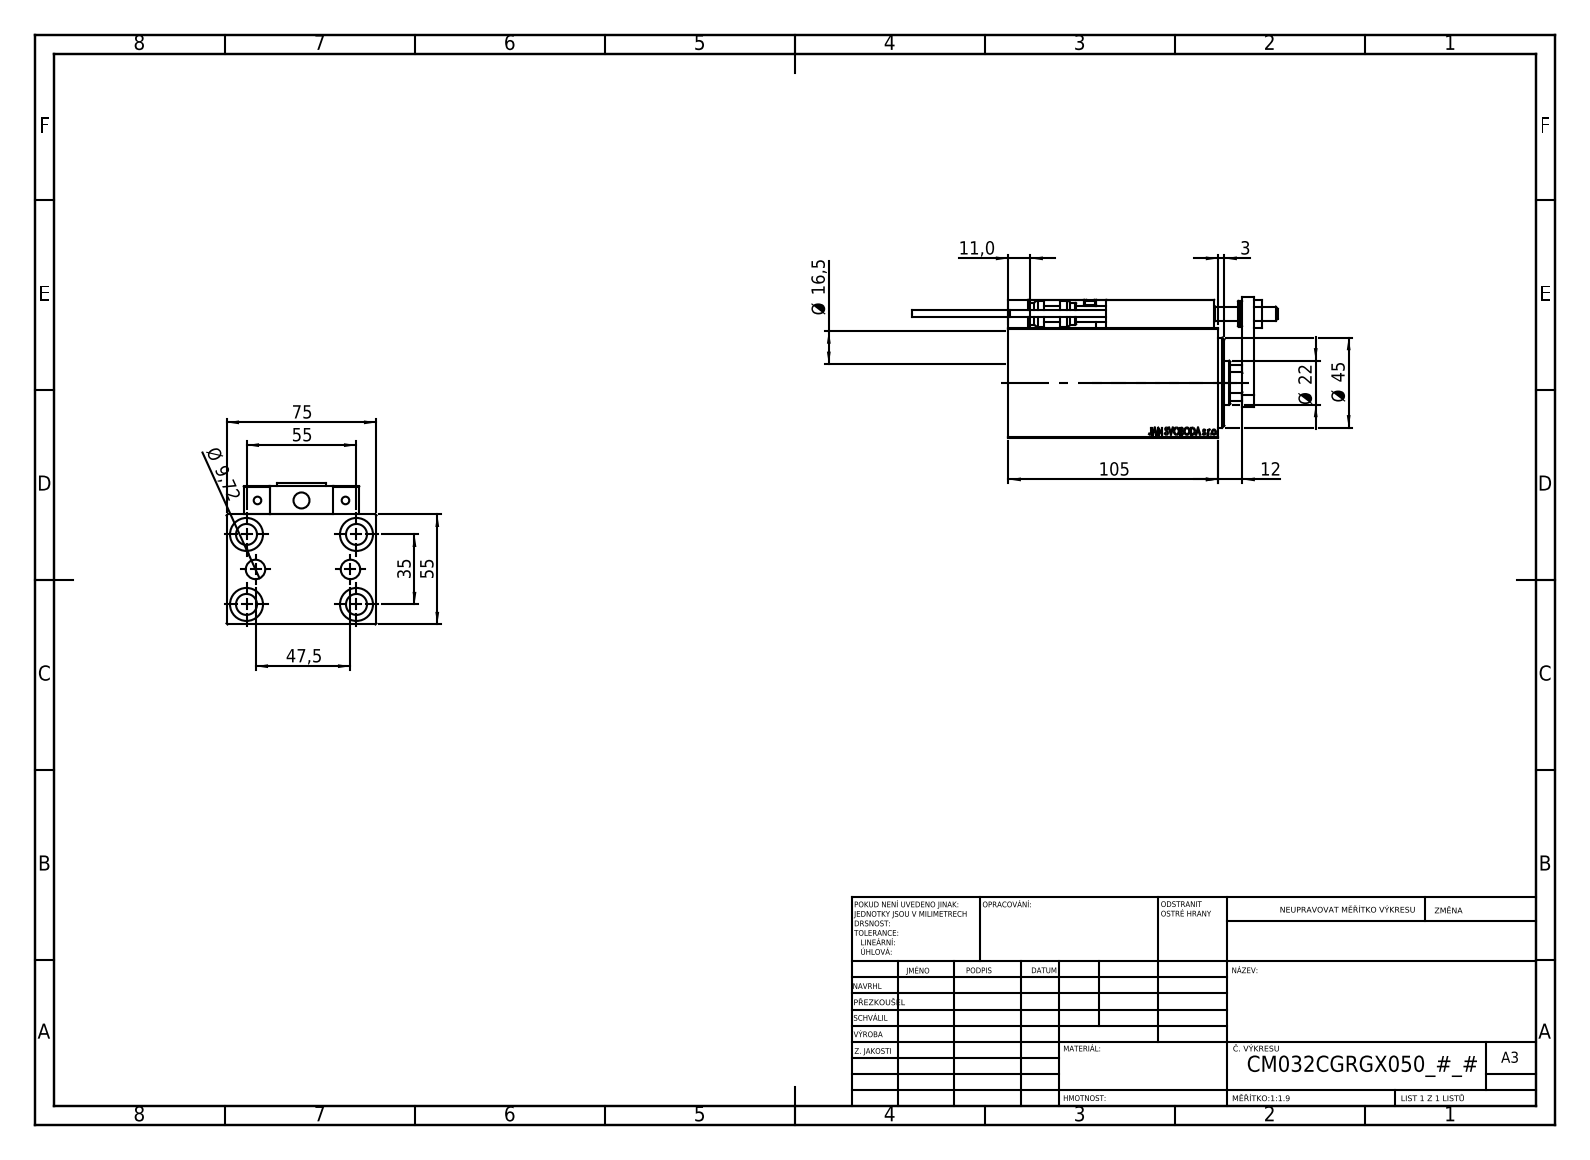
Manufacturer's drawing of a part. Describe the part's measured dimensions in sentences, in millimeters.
The part is named "SWITCH DIM B,W; Block; ALLEN BOLT D5; TYC_L79 (+8 more)". Its 3-D file was written by "SolidWorks 2019 (CONFIG_CONTROL_DESIGN)". It is 23 solids with 1272 faces: 558 planar, 180 cylindrical and 534 other. Overall it measures 182.7 by 75 by 70.5 millimeters. Its volume is 417 640 cubic millimeters and its surface area 101 432 square millimeters. Round holes: 5 of diameter 8, 5 of diameter 10.5, 5 of diameter 16.5, 4 of diameter 3.2, 4 of diameter 4, 2 of diameter 5, 2 of diameter 9.72, 1 of diameter 7, 1 of diameter 22, 1 of diameter 25.5, 1 of diameter 32, 1 of diameter 34. Round bosses or shafts: 2 of diameter 5, 2 of diameter 3.8, 1 of diameter 13, 1 of diameter 11. Partial cylindrical surfaces (rounded edges, fillets, slot ends): 30 of radius 0.3, 2 of radius 3, 1 of radius 10.5. The main face-to-face distances are 55, 75, 14, 10, 12, 69, 7, 5, 15, 25. The hole center spacings are 32.6, 11.37, 17.76, 18.07, 20, 29.59, 29.69, 32.33.
